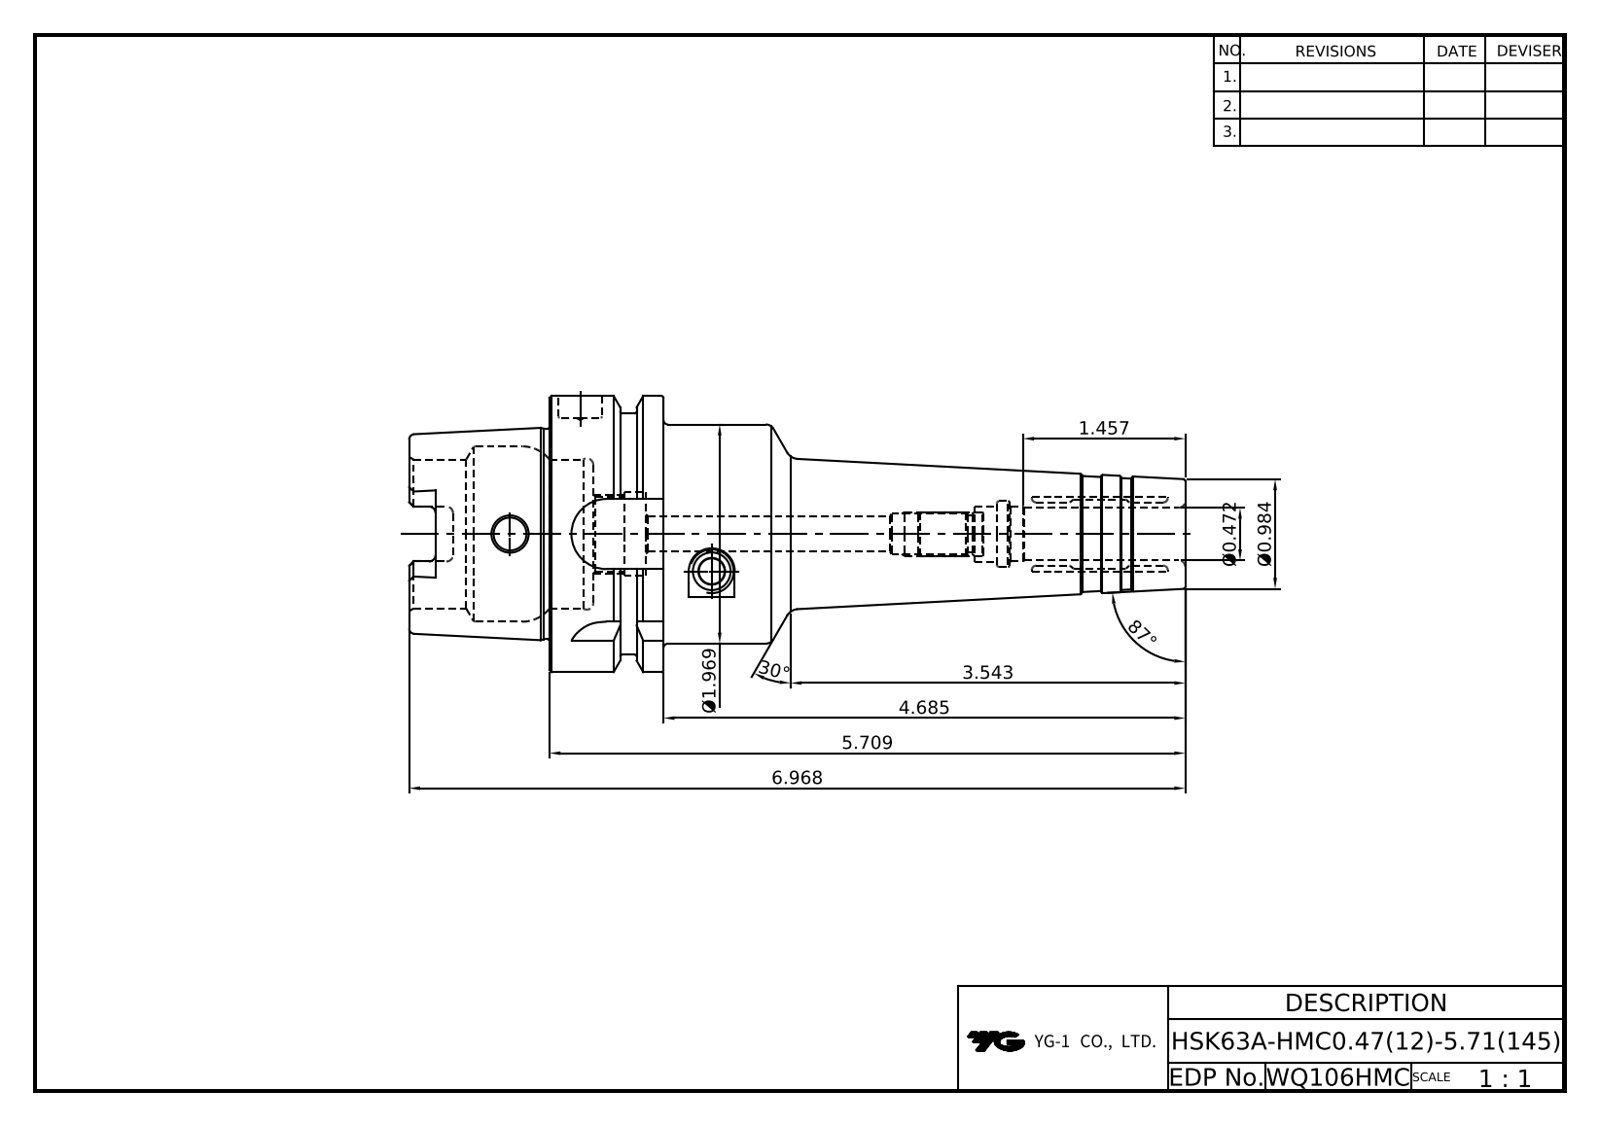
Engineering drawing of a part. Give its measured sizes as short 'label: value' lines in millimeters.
name: LO-HSK63A-HMC12-145
written by: Autodesk Inventor 2020 (AUTOMOTIVE_DESIGN)
unit: mm
bodies: 1 solid, 136 faces (42 planar, 34 cylindrical, 60 other)
size: 177 × 63 × 63
volume: 189 473 mm³; area: 37 824 mm²
holes: 1× ⌀7.5, 1× ⌀8, 1× ⌀8.38, 1× ⌀10, 1× ⌀12, 1× ⌀12.6, 1× ⌀16.92, 1× ⌀19, 1× ⌀34, 1× ⌀40
bosses: 1× ⌀63, 1× ⌀55, 1× ⌀50, 1× ⌀48.04
rounds: 6× R1.5, 4× R2.88, 4× R8
face distances: 26, 10, 16, 32, 42, 58, 177, 145, 135, 119
